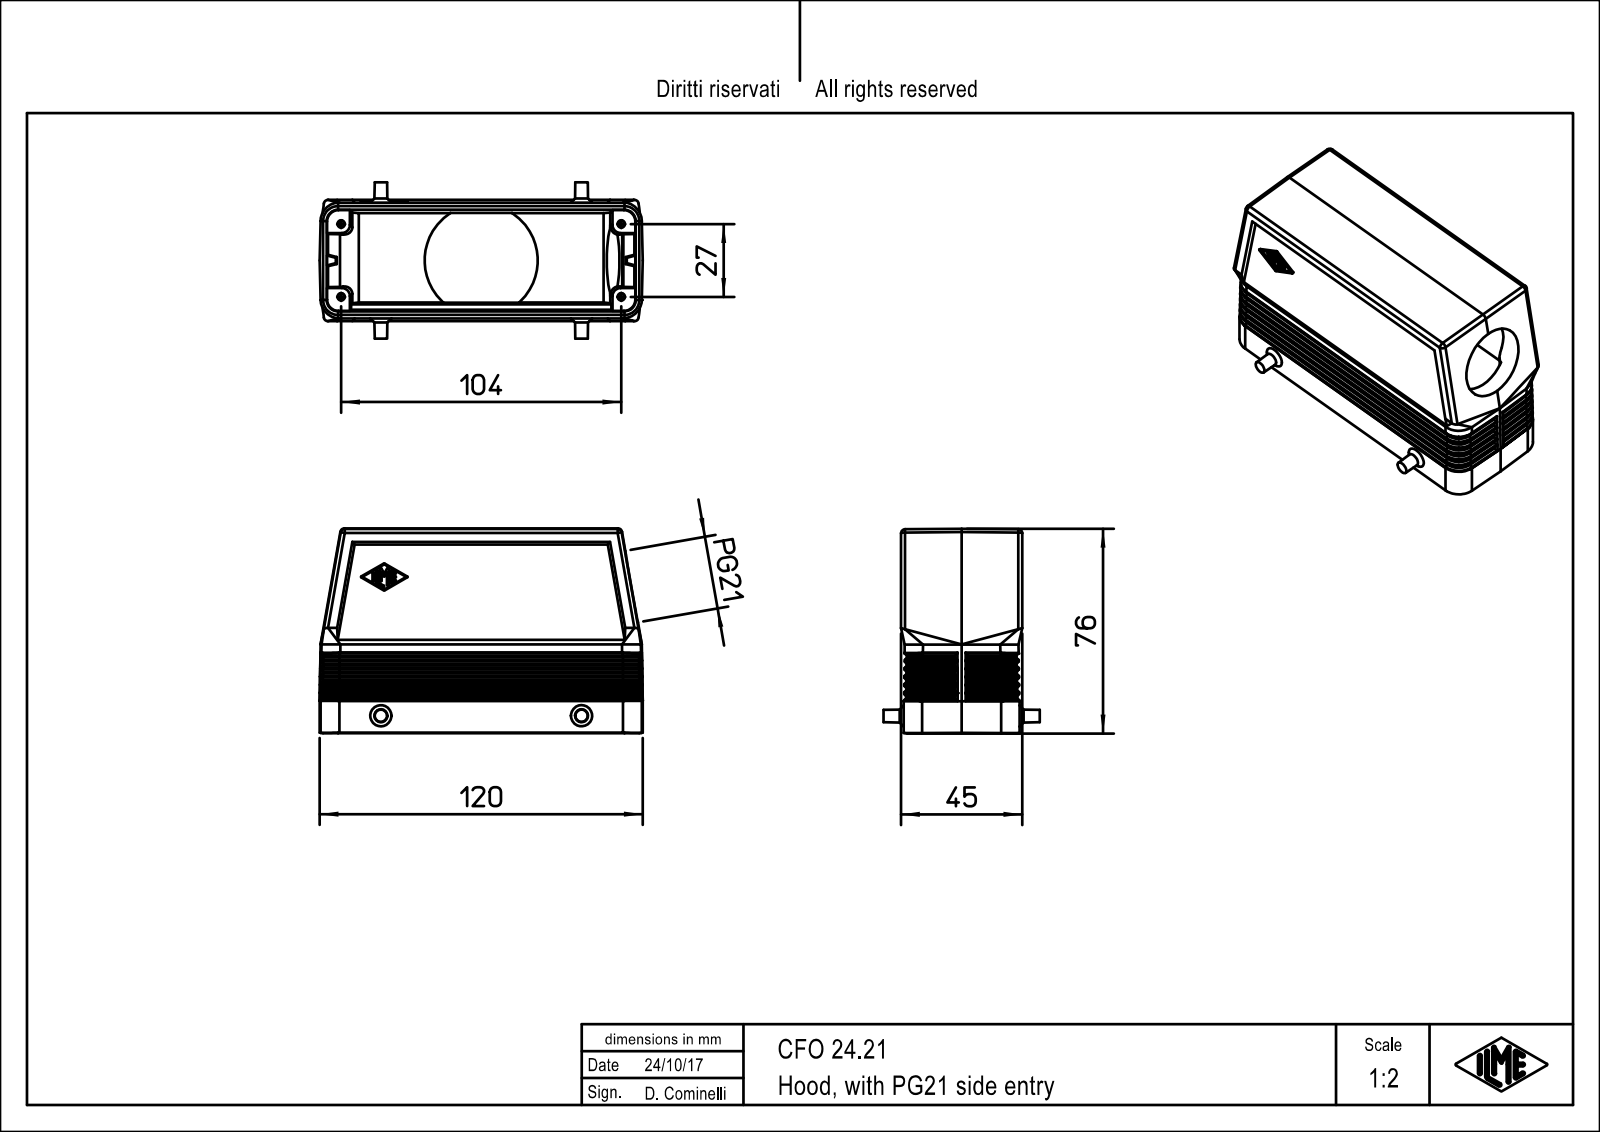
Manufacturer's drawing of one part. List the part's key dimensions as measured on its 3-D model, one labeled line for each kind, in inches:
Part name (STEP PRODUCT): CFO_24.21
STEP written by: PTC Creo Elements/Direct Modeling 19.0E 27-Jun-2016 (C) Parametric Technology GmbH (AUTOMOTIVE_DESIGN)
Units: inches
Bodies: 1 solid, 529 faces (239 planar, 138 cylindrical, 152 other)
Overall size (bounding box): 4.724 × 2.992 × 2.283
Volume: 6.543 in³ · Surface area: 84.37 in²
Round holes (diameter × count): ⌀1.063 ×1
Partial cylindrical surfaces — rounded edges, fillets, slot ends (radius × count): R0.02 ×78, R0.013 ×15, R0.059 ×11, R0.276 ×8, R0.118 ×4, R0.165 ×4, R0.007 ×3, R0.026 ×1
Main face-to-face distances: 1.693, 0.079, 0.079, 0.157, 0.126, 0.039, 1.732, 0.333, 0.236, 0.237
